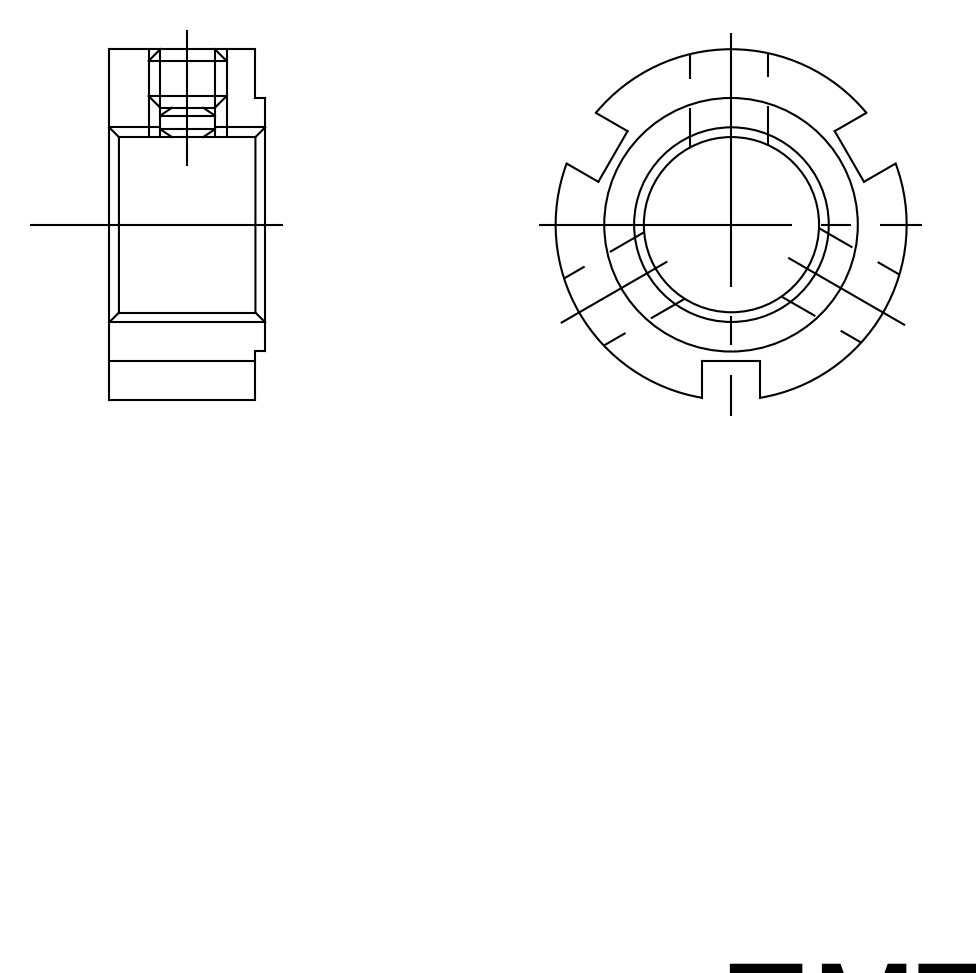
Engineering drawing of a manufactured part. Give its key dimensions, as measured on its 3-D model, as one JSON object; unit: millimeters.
{"part_name": "FKD ZMT 10", "step_written_by": "Autodesk Inventor 2011 (AUTOMOTIVE_DESIGN)", "units": "millimeters", "bodies": {"solids": 1, "faces": 20, "planar": 12, "cylindrical": 8, "other": 0}, "overall_size": [18, 17.87, 8], "volume_mm3": 1115, "surface_area_mm2": 1171, "round_holes": [[3.24, 3], [10, 1]], "round_bosses_or_shafts": [[18, 1], [13, 1]], "face_to_face_distances": [7.5, 0.5, 8, 3]}
